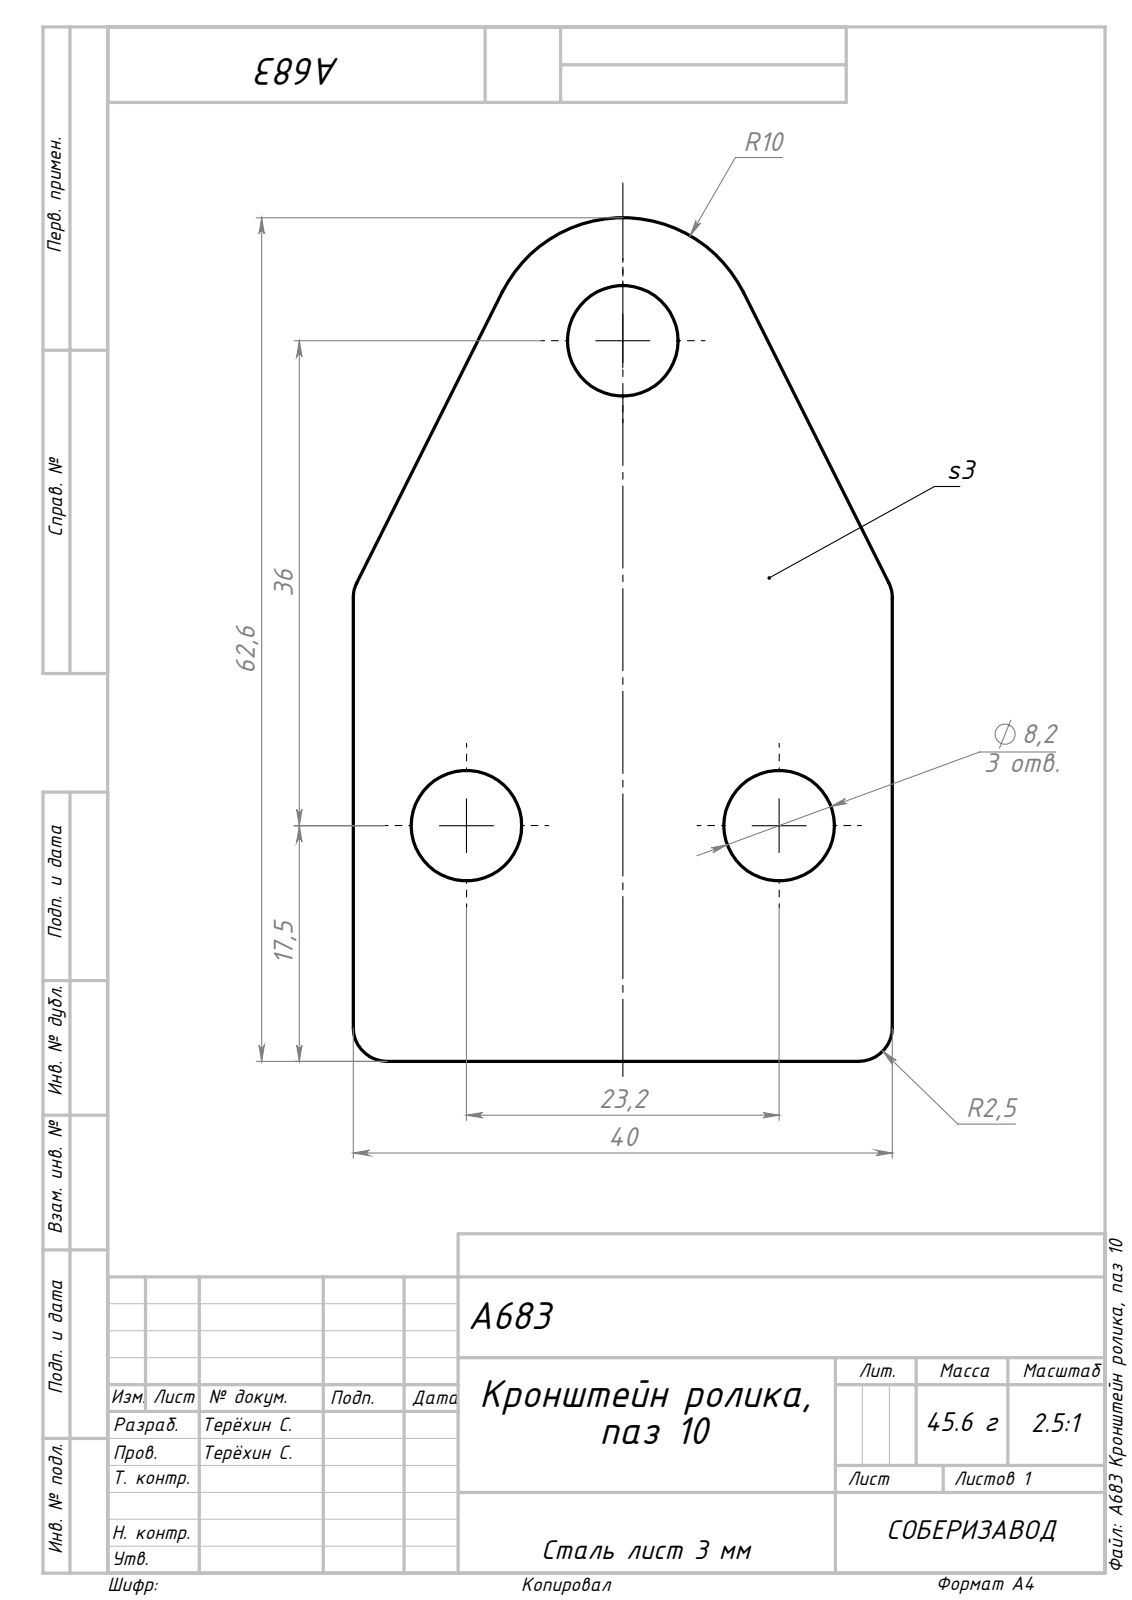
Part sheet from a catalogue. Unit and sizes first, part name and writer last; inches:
Units: inches
Overall size (bounding box): 2.466 × 1.575 × 0.118
Round holes (diameter × count): ⌀0.323 ×3
Partial cylindrical surfaces — rounded edges, fillets, slot ends (radius × count): R0.098 ×4, R0.394 ×1
Main face-to-face distances: 0.118, 1.575
Hole centre spacings: 1.489, 0.913
Volume: 0.357 in³ · Surface area: 7.237 in²
Bodies: 1 solid, 18 faces (7 planar, 11 cylindrical, 0 other)
Part name (STEP PRODUCT): A683 Кронштейн ролика, паз 10
STEP written by: SolidWorks 2022 (AUTOMOTIVE_DESIGN)
